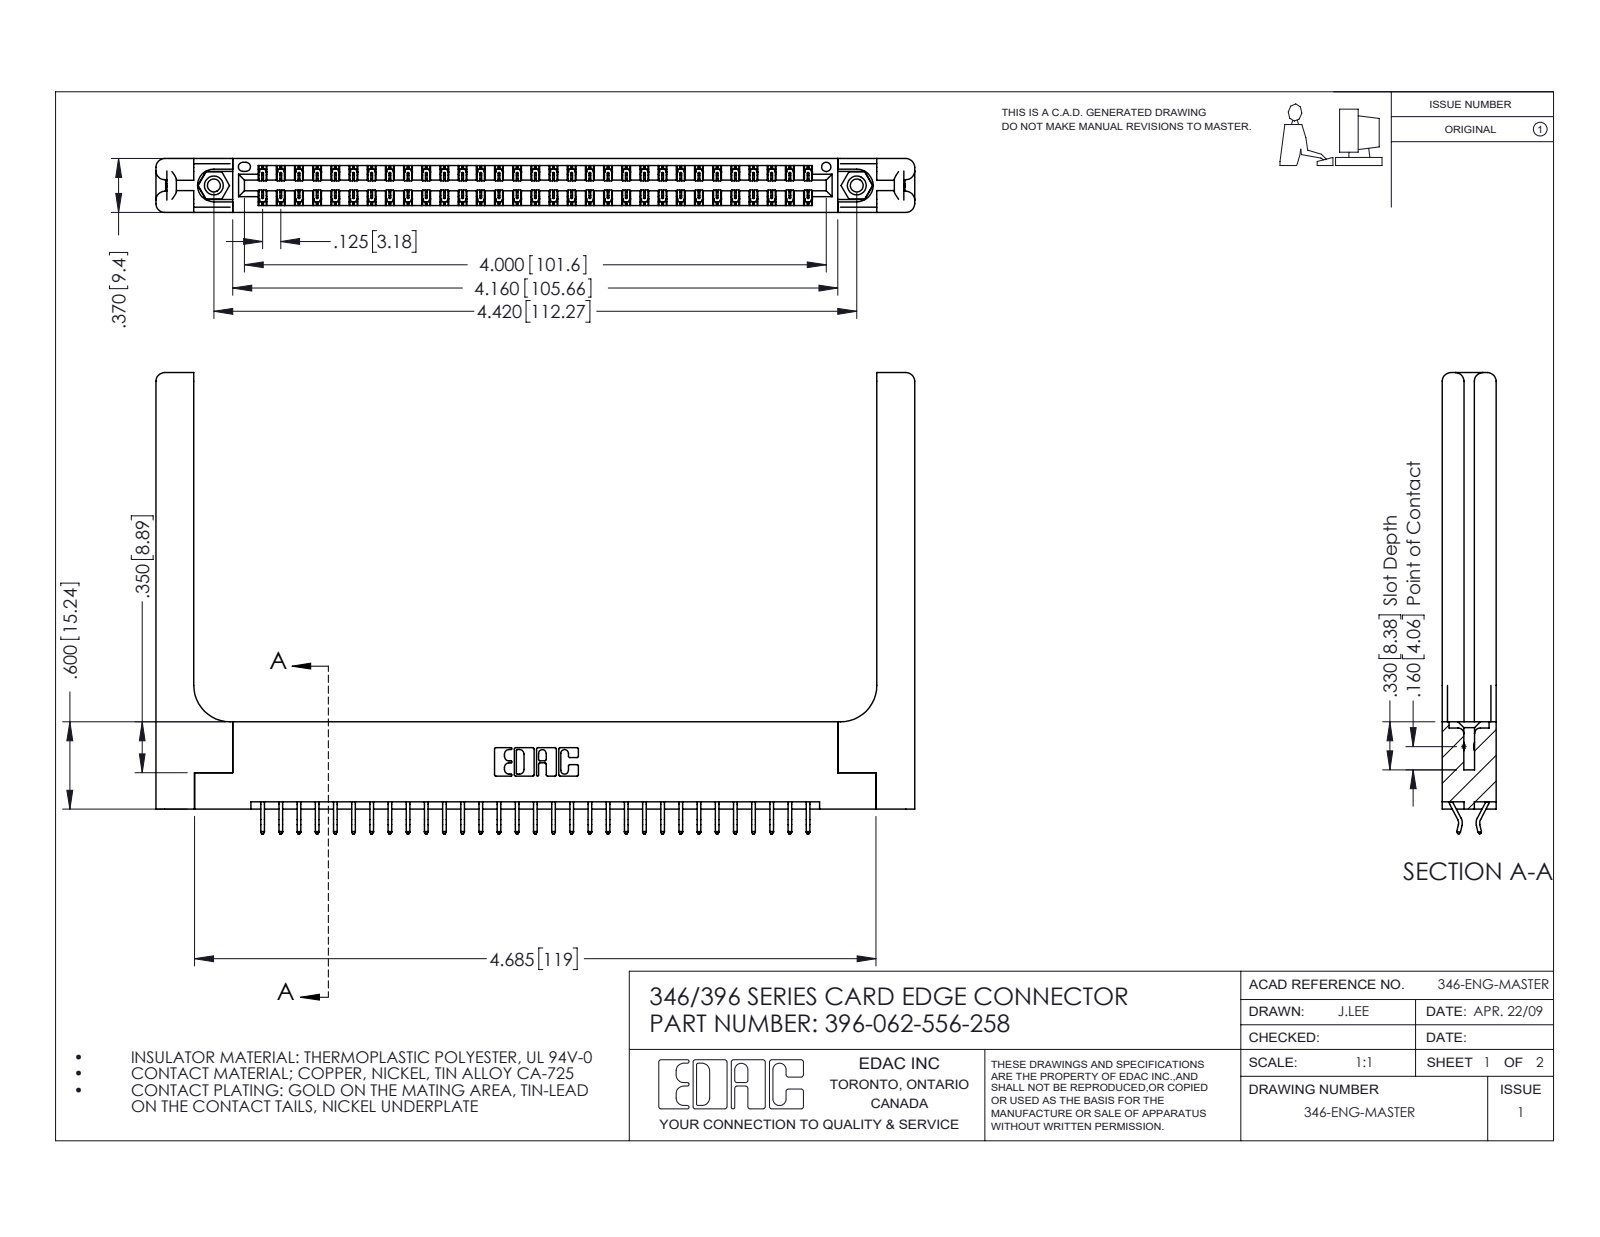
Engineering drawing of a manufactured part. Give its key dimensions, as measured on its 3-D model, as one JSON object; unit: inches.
{"part_name": "346-220-058_345-220-058; 346 Part_Flush Mounting Lugs - 0.156 Dia-TH; 345-250-001_345-250-001-102; 396-062-556-258 (+1 more)", "step_written_by": "SolidWorks 2016 (CONFIG_CONTROL_DESIGN)", "units": "inches", "bodies": {"solids": 67, "faces": 3974, "planar": 2642, "cylindrical": 1272, "other": 60}, "overall_size": [5.216, 3.17, 0.37], "volume_in3": 1.24, "surface_area_in2": 34.69, "round_holes": [[0.089, 2], [0.125, 2], [0.156, 2], [0.064, 1]], "round_bosses_or_shafts": [[0.155, 2]], "partial_cylinders_radius": [[0.006, 93], [0.01, 22], [0.06, 16], [0.007, 6], [0.031, 6], [0.026, 3], [0.01, 2], [0.014, 2]], "face_to_face_distances": [0.37, 0.048, 0.322, 0.072, 0.148, 0.15, 0.25, 0.025, 0.298, 0.275], "hole_center_spacings": [0.246, 4.212, 4.42]}
